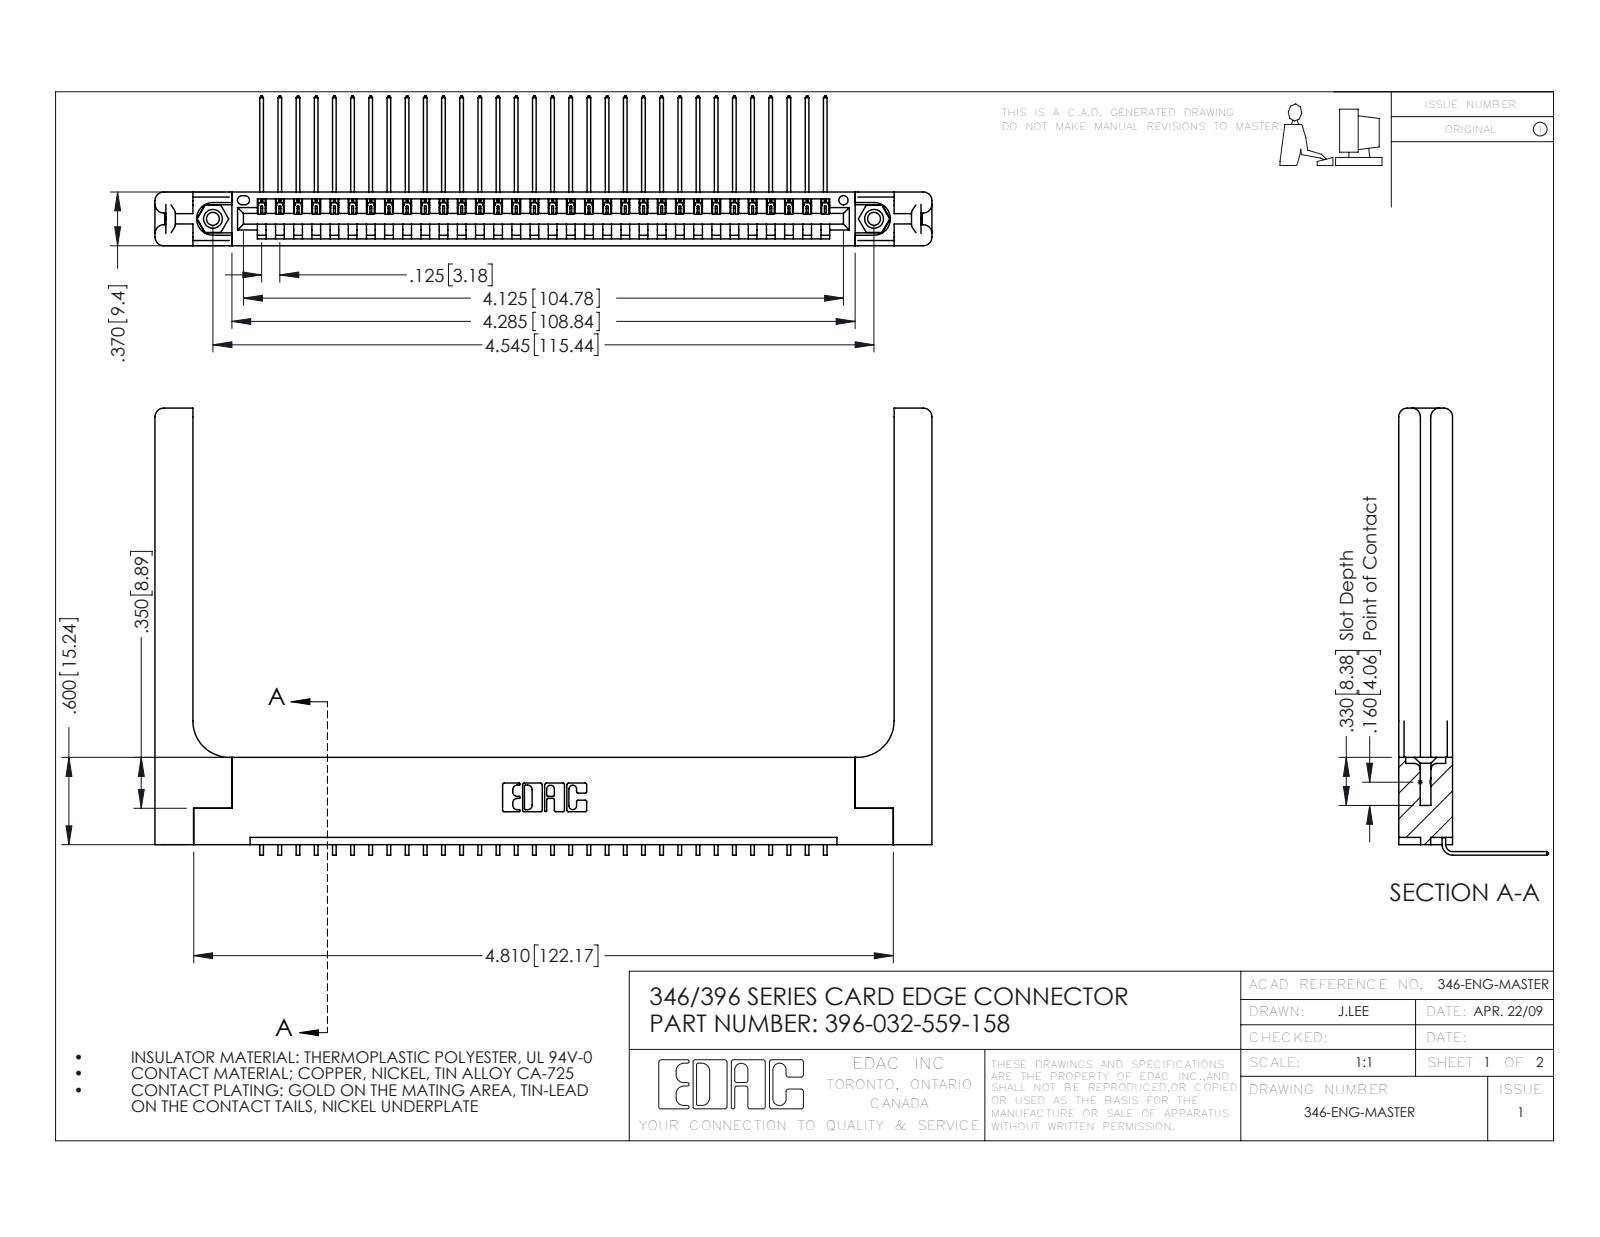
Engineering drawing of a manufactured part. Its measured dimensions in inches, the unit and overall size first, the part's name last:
Units: inches
Overall size (bounding box): 5.341 × 3.073 × 1.03
Round holes (diameter × count): ⌀0.089 ×2, ⌀0.125 ×2, ⌀0.156 ×2, ⌀0.064 ×1
Round bosses / shafts (diameter × count): ⌀0.155 ×2
Partial cylindrical surfaces — rounded edges, fillets, slot ends (radius × count): R0.006 ×64, R0.01 ×22, R0.06 ×16, R0.007 ×6, R0.031 ×6, R0.026 ×3, R0.03 ×2, R0.031 ×2
Main face-to-face distances: 0.37, 0.048, 0.072, 0.322, 0.148, 0.15, 0.025, 0.25, 0.298, 0.222
Hole centre spacings: 0.246, 4.337, 4.545
Volume: 1.254 in³ · Surface area: 34.06 in²
Bodies: 37 solids, 2298 faces (1568 planar, 670 cylindrical, 60 other)
Part name (STEP PRODUCT): 346-220-058_345-220-058; 345-250-001_345-250-001-102; 345-292-001_558 559 Tail - 1; 396-032-559-158 (+1 more)
STEP written by: SolidWorks 2016 (CONFIG_CONTROL_DESIGN)
